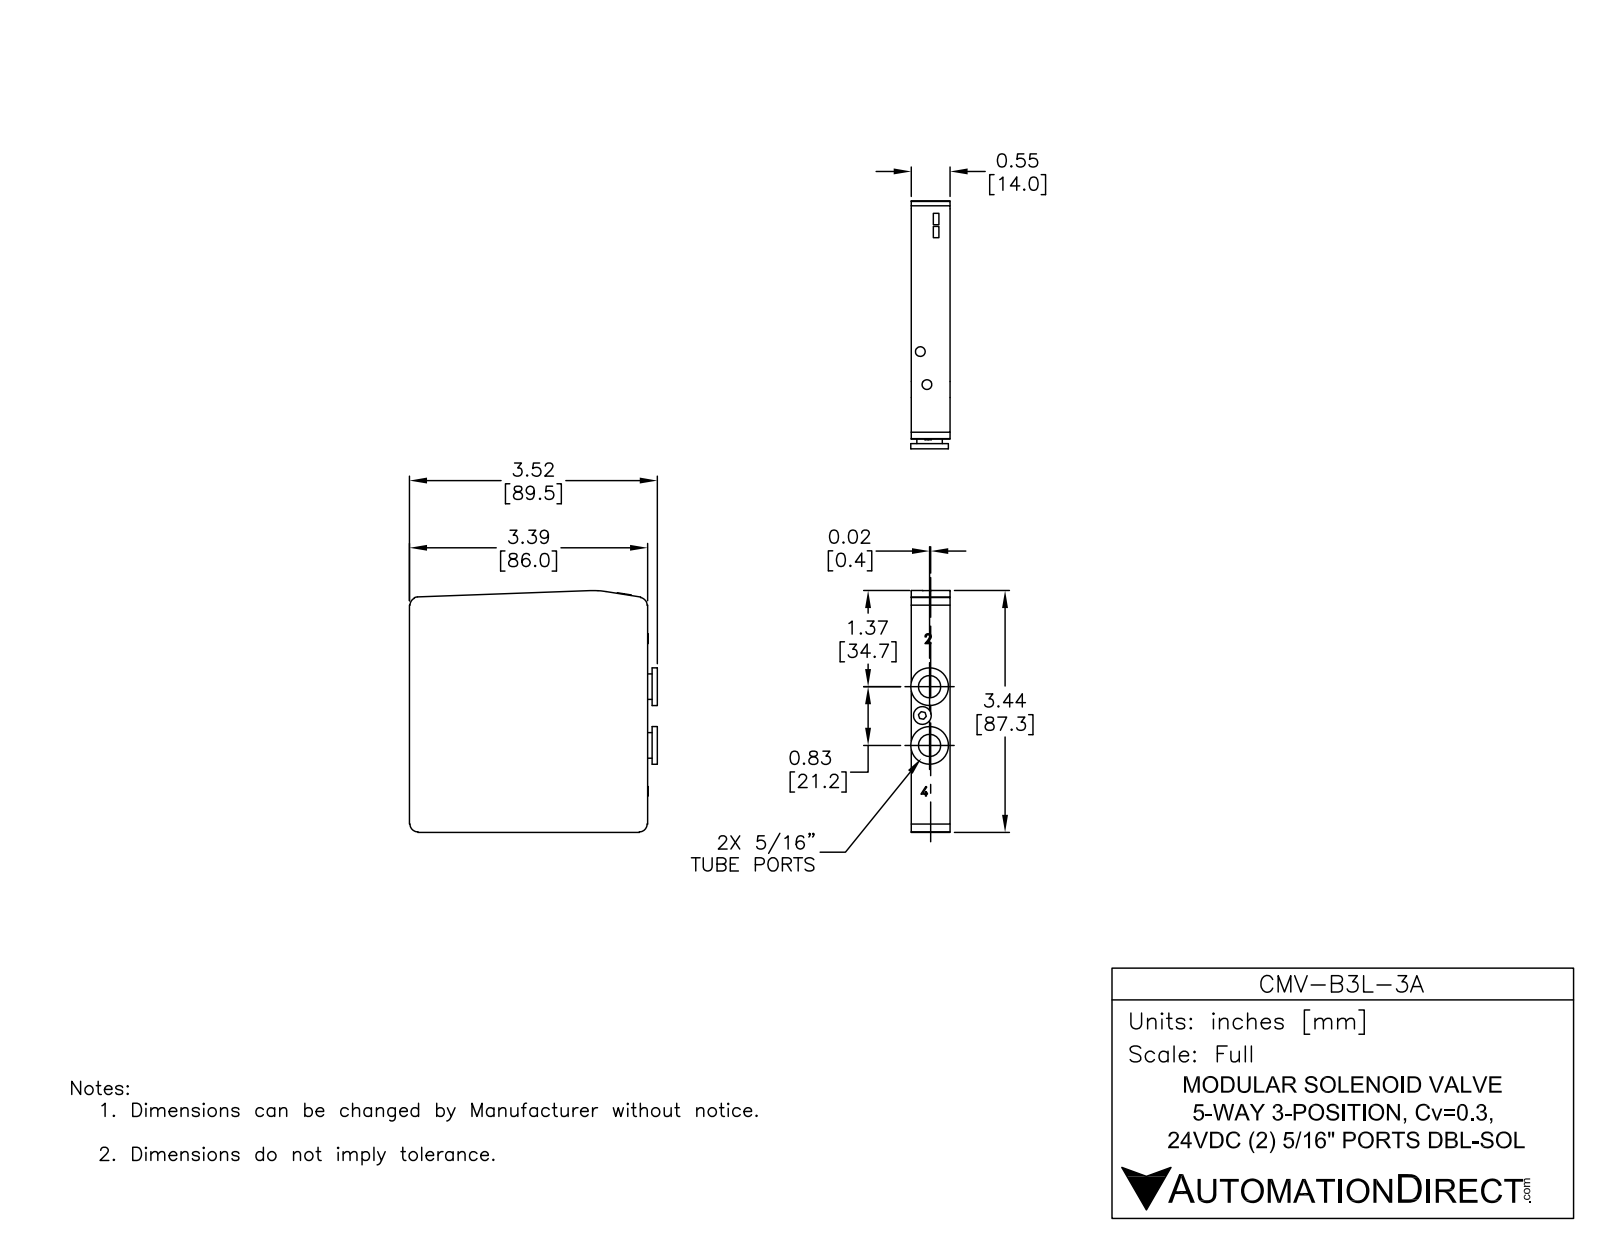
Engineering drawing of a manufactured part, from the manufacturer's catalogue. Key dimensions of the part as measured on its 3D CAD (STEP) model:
Part name (STEP PRODUCT): CMV-B3L-3A
STEP written by: SolidWorks 2013 (AUTOMOTIVE_DESIGN)
Units: millimetres
Bodies: 78 solids, 1158 faces (875 planar, 162 cylindrical, 121 other)
Overall size (bounding box): 89.5 × 87.3 × 22.93
Volume: 95 434 mm³ · Surface area: 47 242 mm²
Round holes (diameter × count): ⌀5.25 ×4, ⌀3.35 ×2, ⌀4.4 ×2, ⌀6.5 ×2, ⌀8 ×2, ⌀9.8 ×2, ⌀11.5 ×2, ⌀3.6 ×1, ⌀4.5 ×1, ⌀6.25 ×1, ⌀6.4 ×1
Round bosses / shafts (diameter × count): ⌀1.5 ×4, ⌀13.6 ×2, ⌀9.2 ×2, ⌀6.25 ×2, ⌀5.75 ×2, ⌀4.2 ×2, ⌀4 ×2, ⌀3.5 ×1
Partial cylindrical surfaces — rounded edges, fillets, slot ends (radius × count): R2.35 ×12, R0.78 ×4, R1.5 ×4, R2.8 ×4, R1 ×2, R0.15 ×1, R0.17 ×1, R0.25 ×1
Main face-to-face distances: 14, 4, 10, 3, 1, 83, 5, 15, 29.75, 14.33
Hole centre spacings: 9.7, 19.98, 22.17, 8.66, 8.67, 8.68, 9.46, 10.61
